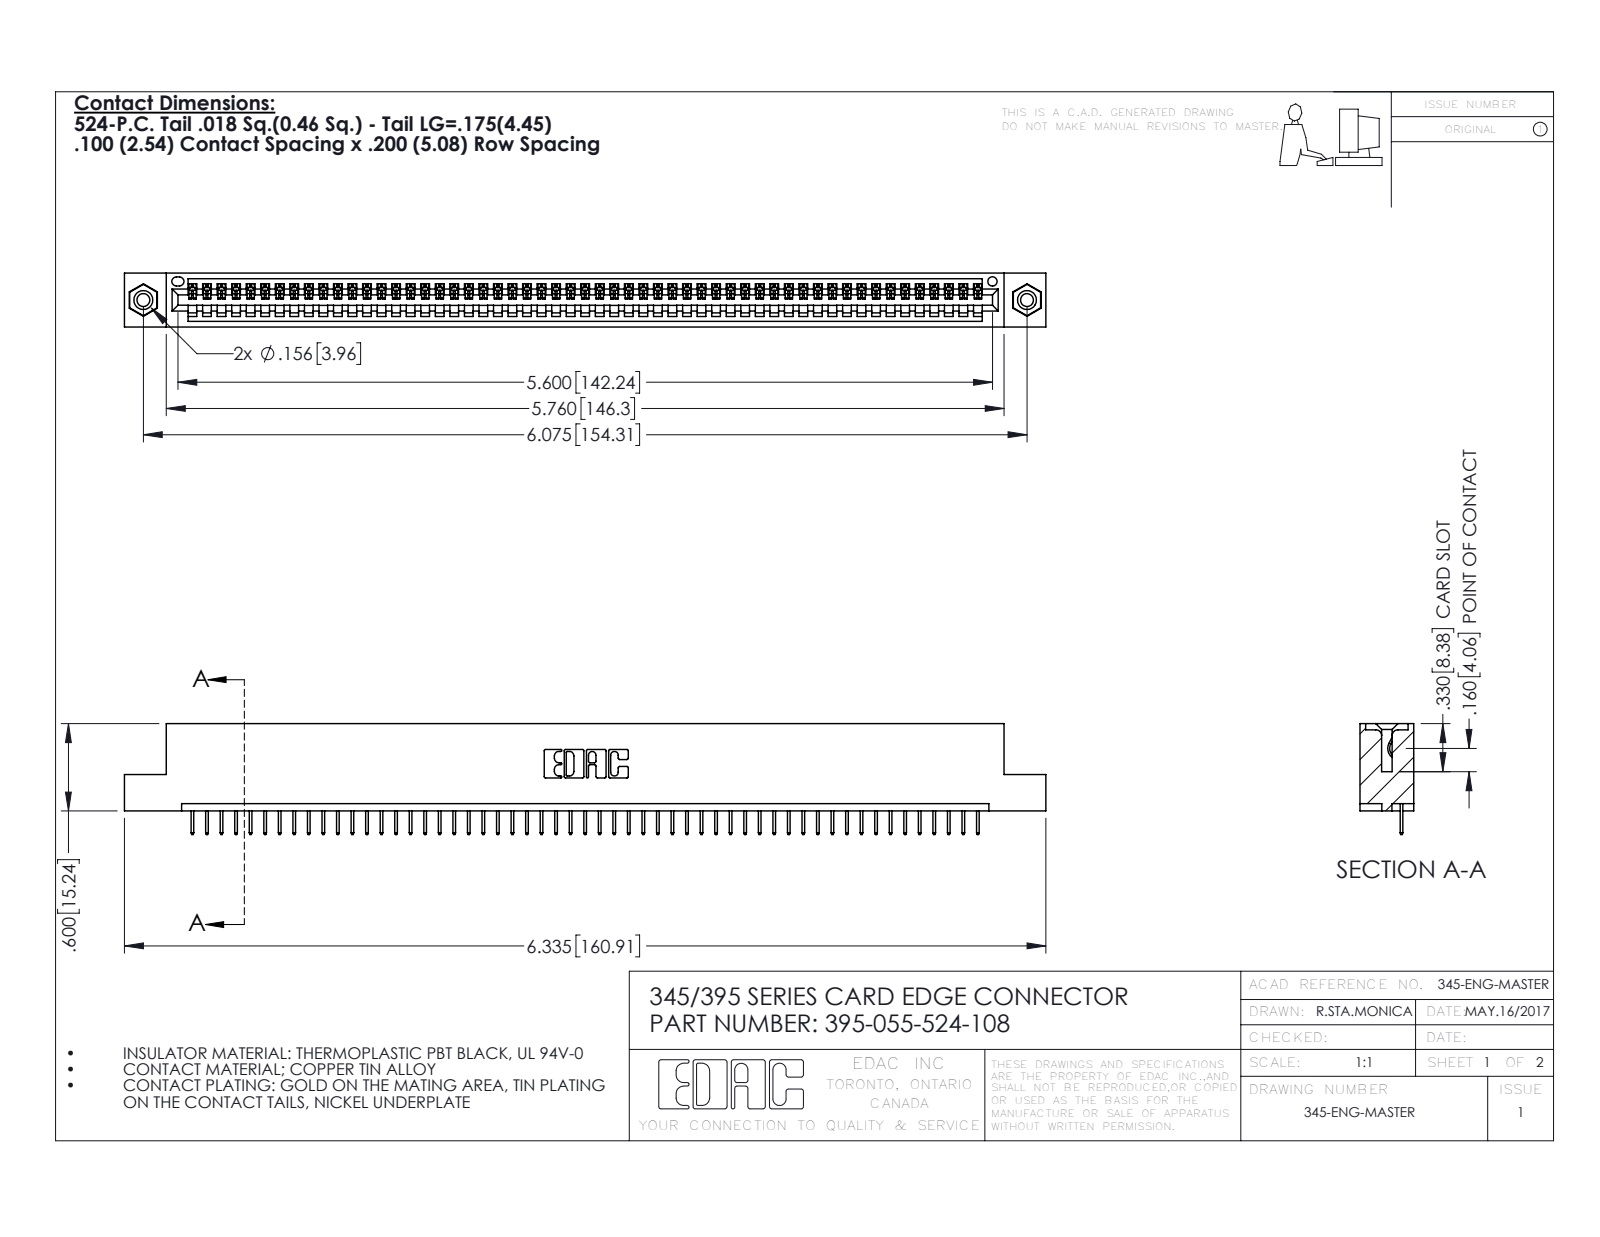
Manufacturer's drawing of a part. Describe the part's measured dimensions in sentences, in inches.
The part is named "345-292-001_345-293-124; 395-055-524-108; 345-250-001_345-250-003-102; 345 Part_Flush Mounting Lugs - 0.156 Dia-TI". Its 3-D file was written by "SolidWorks 2016 (CONFIG_CONTROL_DESIGN)". It is 58 solids with 3596 faces: 2642 planar, 938 cylindrical and 16 other. Overall it measures 6.335 by 0.762 by 0.37 inches. Its volume is 0.925 cubic inches and its surface area 30.47 square inches. Round holes: 2 of diameter 0.089, 2 of diameter 0.125, 2 of diameter 0.156, 1 of diameter 0.064. Round bosses or shafts: 2 of diameter 0.155. Partial cylindrical surfaces (rounded edges, fillets, slot ends): 110 of radius 0.006, 22 of radius 0.01, 6 of radius 0.007, 6 of radius 0.031, 3 of radius 0.026, 2 of radius 0.031, 2 of radius 0.04, 1 of radius 0.014. The main face-to-face distances are 0.072, 0.298, 0.37, 0.2, 0.098, 0.272, 0.025, 0.225, 0.072, 0.149. The hole center spacings are 0.27, 5.839, 6.075.
